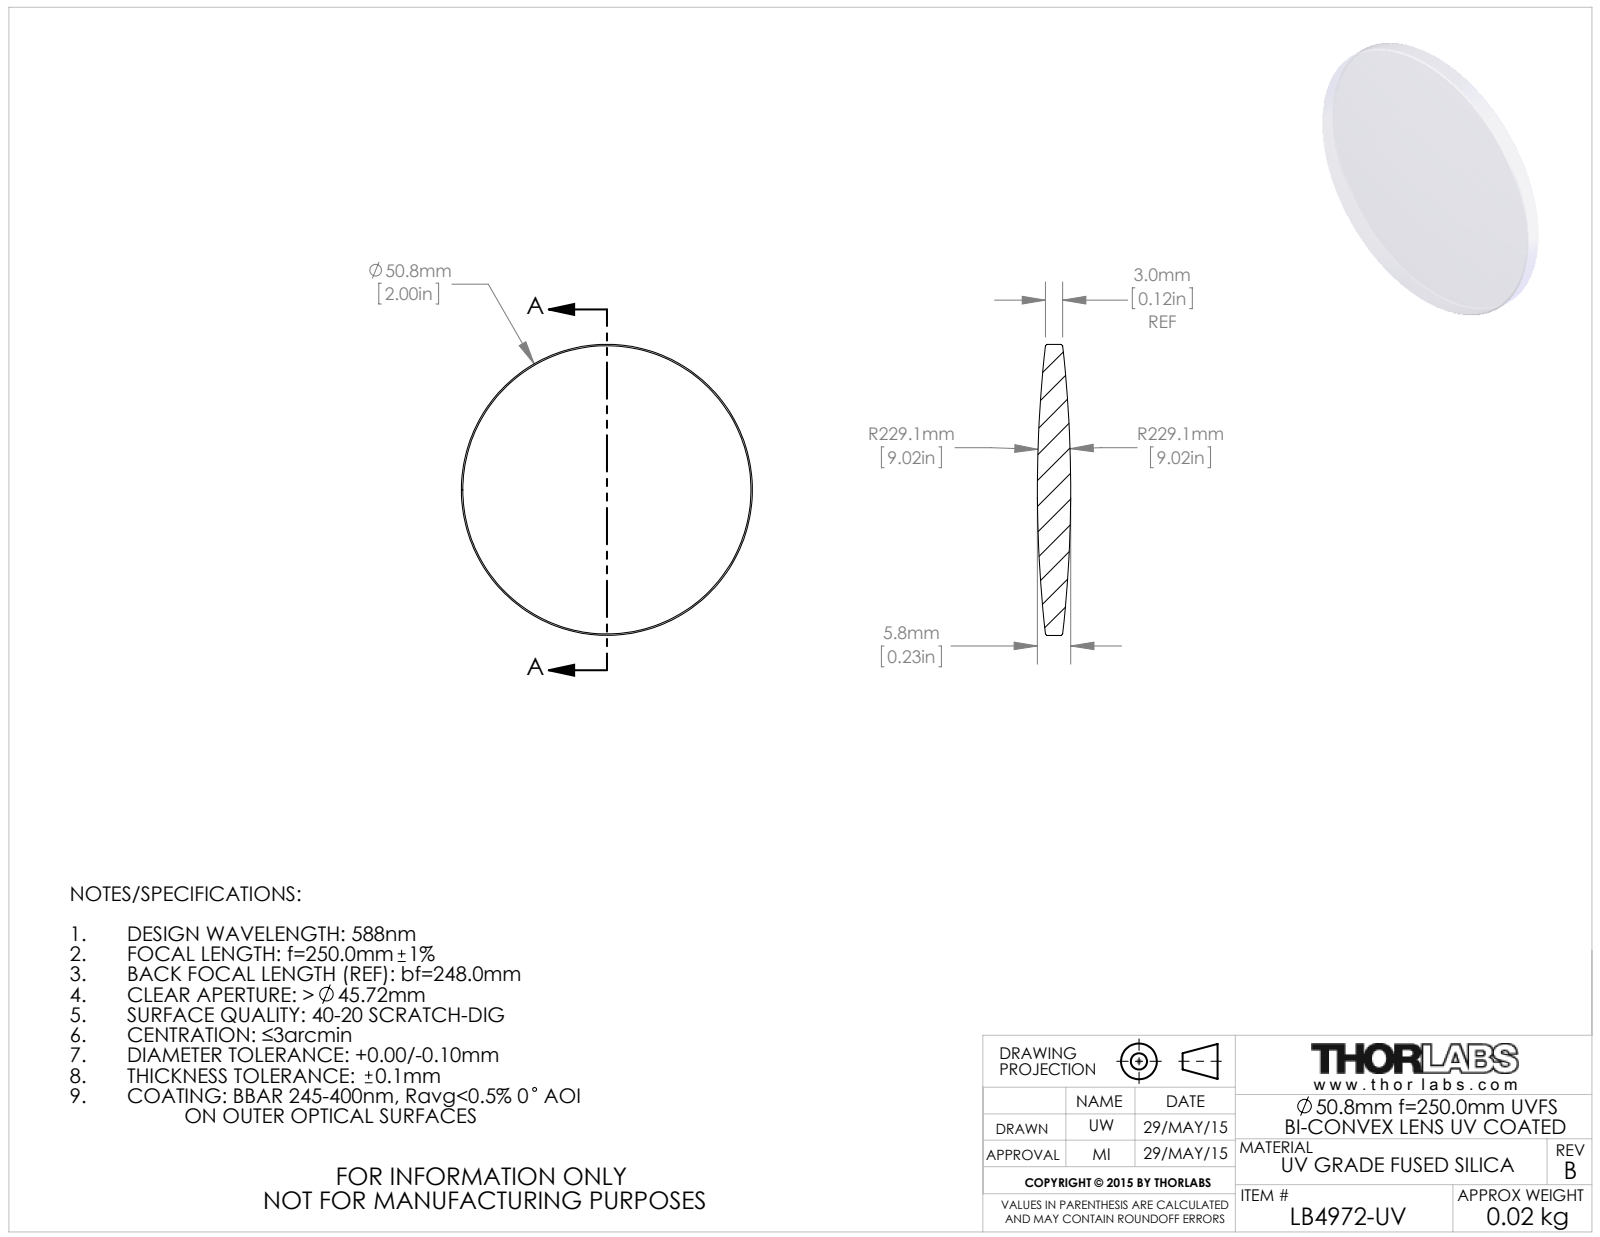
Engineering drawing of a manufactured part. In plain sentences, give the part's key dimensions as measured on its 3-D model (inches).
The part is named "4336-E0W". Its 3-D file was written by "SolidWorks 2014 (CONFIG_CONTROL_DESIGN)". It is 1 solid with 10 faces: 0 planar, 2 cylindrical and 8 other. Overall it measures 2 by 2 by 0.228 inches. Its volume is 0.542 cubic inches and its surface area 6.975 square inches. Round bosses or shafts: 1 of diameter 2.
